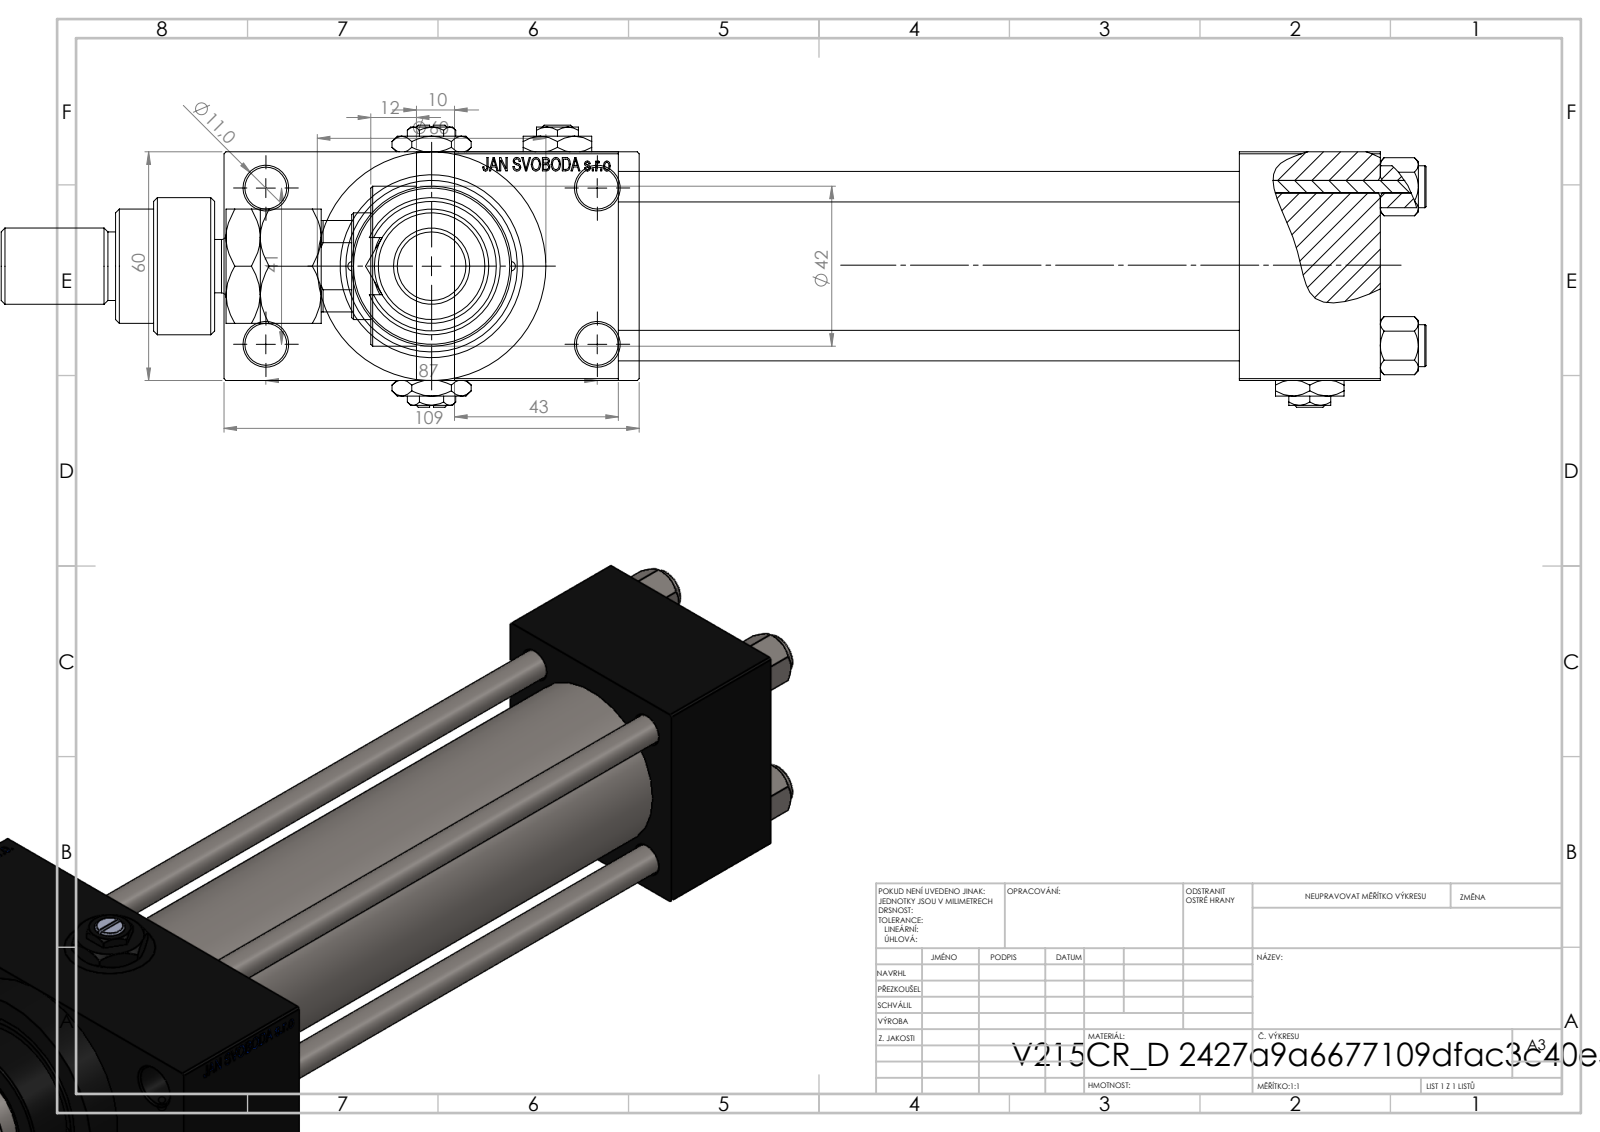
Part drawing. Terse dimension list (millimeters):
name: FEMALE_PART_FOR_DFA; Zatka_pro_OIL_PORT; V215CR_VCP_D; V215_VC_A (+4 more)
written by: SolidWorks 2019 (CONFIG_CONTROL_DESIGN)
unit: mm
bodies: 15 solids, 1284 faces (574 planar, 106 cylindrical, 604 other)
size: 374 × 109 × 74
volume: 714 051 mm³; area: 191 008 mm²
holes: 4× ⌀8, 4× ⌀11, 2× ⌀2.5, 2× ⌀7, 2× ⌀16.66, 2× ⌀24, 1× ⌀18.5, 1× ⌀28, 1× ⌀31, 1× ⌀40, 1× ⌀45
bosses: 4× ⌀11, 1× ⌀60, 1× ⌀46, 1× ⌀42, 1× ⌀36, 1× ⌀30, 1× ⌀22, 1× ⌀20
rounds: 1× R7.5, 1× R12, 1× R13.5
face distances: 60, 24.5, 84.5, 163, 37, 200, 43, 243, 206, 109
hole spacings: 20.85, 22.65, 29.49, 30.62, 41.7, 46.53, 47.15, 48.09
